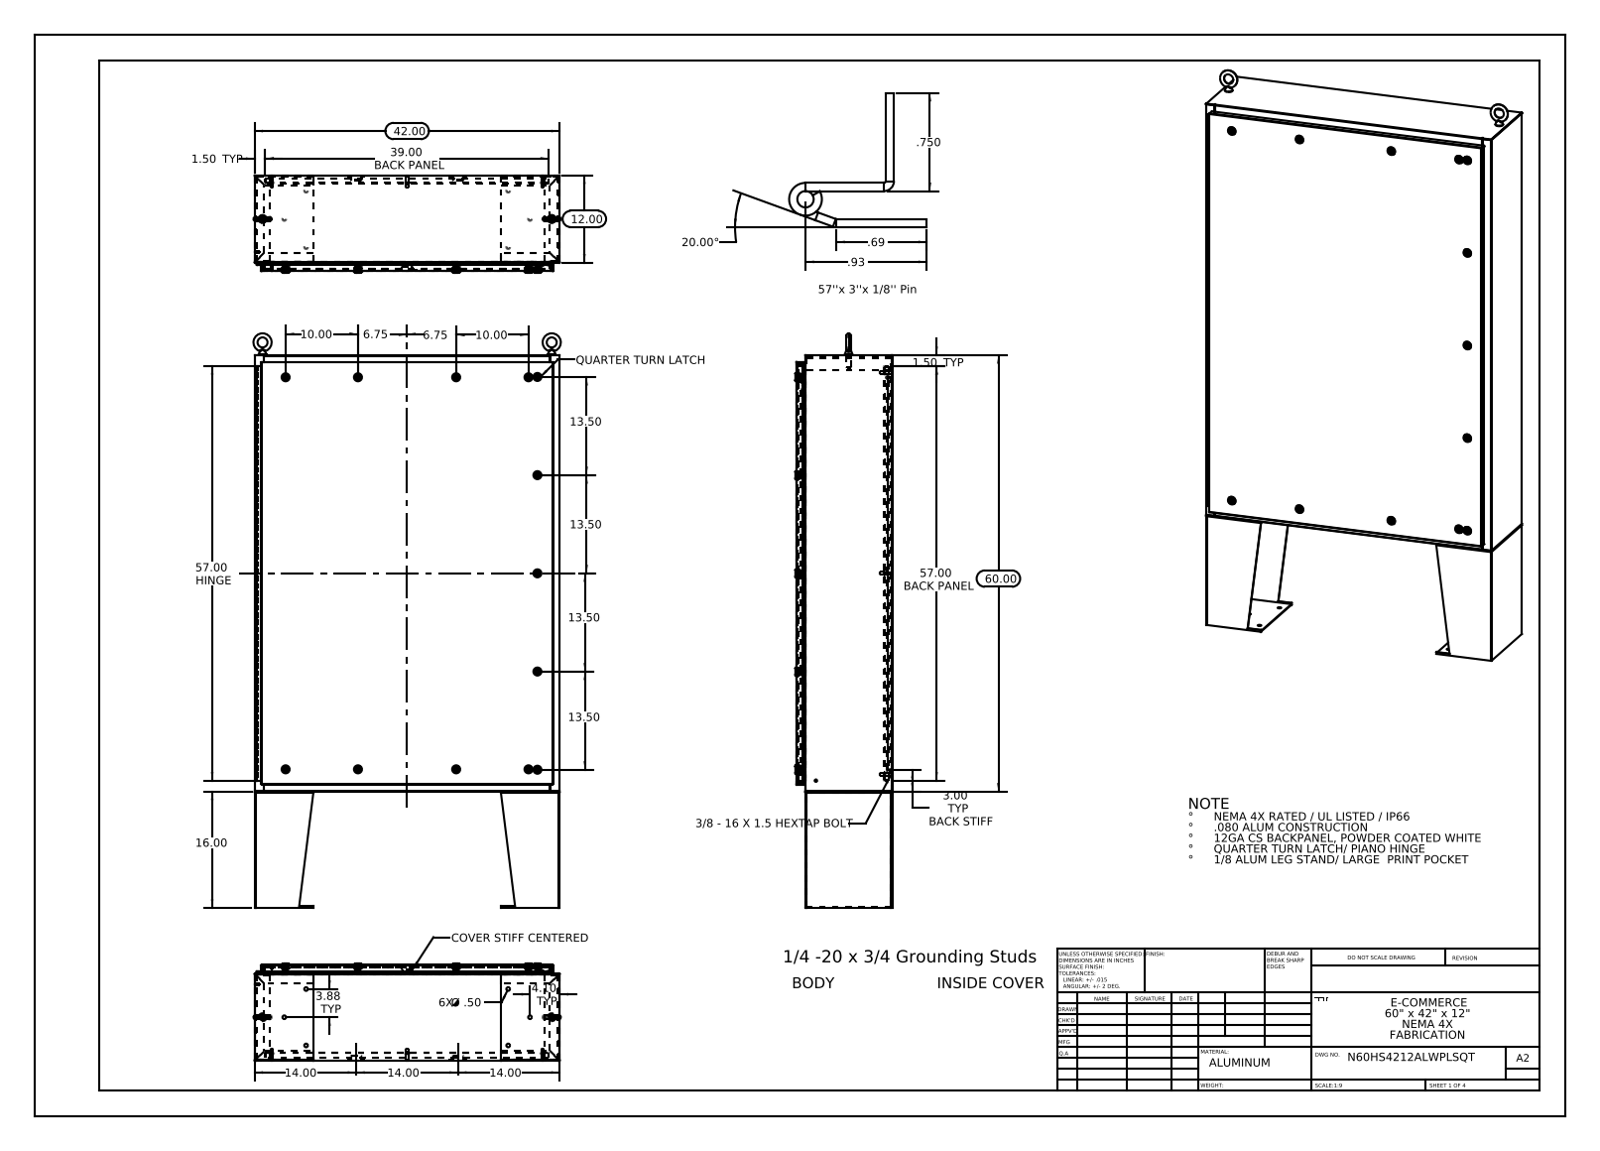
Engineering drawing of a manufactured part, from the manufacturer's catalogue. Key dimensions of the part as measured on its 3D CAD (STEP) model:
Part name (STEP PRODUCT): N60HS4212SSWPLSQT Cover; N60HS4212SSWPLSQT Bottom; HW-EYE-NH-20425_3014T52; 10_30 CD Stud (+8 more)
STEP written by: SolidWorks 2013 (CONFIG_CONTROL_DESIGN)
Units: inches
Bodies: 36 solids, 2379 faces (1197 planar, 986 cylindrical, 196 other)
Overall size (bounding box): 79 × 42.271 × 13.201
Volume: 1 017 in³ · Surface area: 24 510 in²
Round holes (diameter × count): ⌀0.5 ×14, ⌀0.25 ×8, ⌀0.75 ×4, ⌀0.125 ×1, ⌀0.125 ×1
Round bosses / shafts (diameter × count): ⌀0.625 ×10, ⌀0.375 ×8, ⌀0.33 ×8, ⌀0.157 ×8, ⌀0.14 ×8, ⌀0.315 ×2, ⌀0.236 ×2, ⌀0.25 ×1
Partial cylindrical surfaces — rounded edges, fillets, slot ends (radius × count): R0.013 ×36, R0.088 ×30, R0.442 ×13, R0.039 ×8, R0.143 ×8, R0.019 ×6, R0.117 ×4, R0.125 ×4
Main face-to-face distances: 0.075, 13.126, 0.104, 13.051, 1.075, 13.201, 1, 12.126, 12.051, 1.179
Hole centre spacings: 2.225, 7.137, 27.625, 31.035, 33.317, 34.004, 34.006, 46.376
